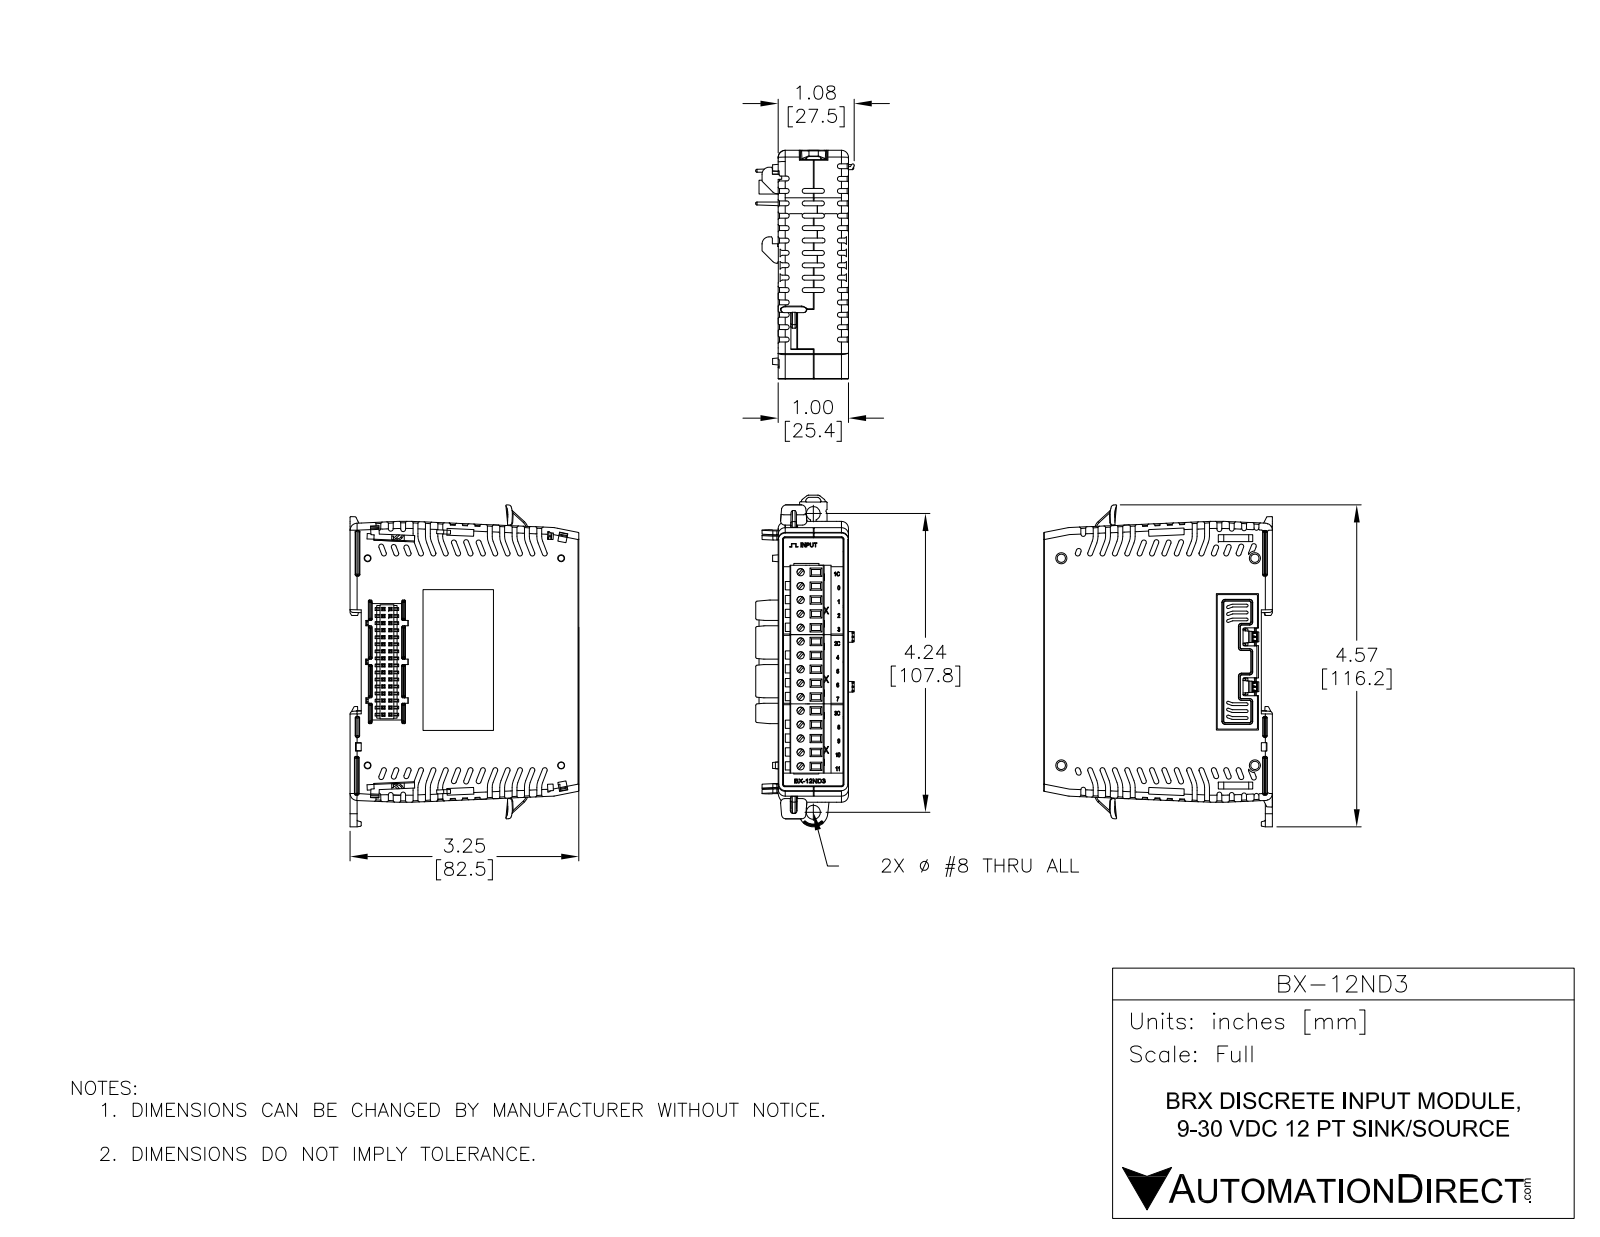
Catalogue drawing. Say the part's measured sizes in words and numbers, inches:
The part is named "BX-12ND3". Its 3-D file was written by "SolidWorks 2017 (AUTOMOTIVE_DESIGN)". It is 15 solids with 3762 faces: 2658 planar, 573 cylindrical and 531 other. Overall it measures 4.586 by 3.311 by 1.402 inches. Its volume is 11.6 cubic inches and its surface area 72.79 square inches. Round holes: 2 of diameter 0.047, 2 of diameter 0.065, 2 of diameter 0.118, 2 of diameter 0.118, 1 of diameter 0.199. Round bosses or shafts: 2 of diameter 0.062, 2 of diameter 0.059. Partial cylindrical surfaces (rounded edges, fillets, slot ends): 102 of radius 0.005, 47 of radius 0.01, 34 of radius 0.02, 24 of radius 0.005, 21 of radius 0.008, 15 of radius 0.122, 14 of radius 0.117, 13 of radius 0.039. The main face-to-face distances are 1, 3.211, 0.1, 3.22, 0.475, 0.157, 3.053, 3.063, 0.787, 0.63. The hole center spacings are 0.1, 0.824, 0.919, 1.3, 2.093, 2.193, 2.585, 2.617.
